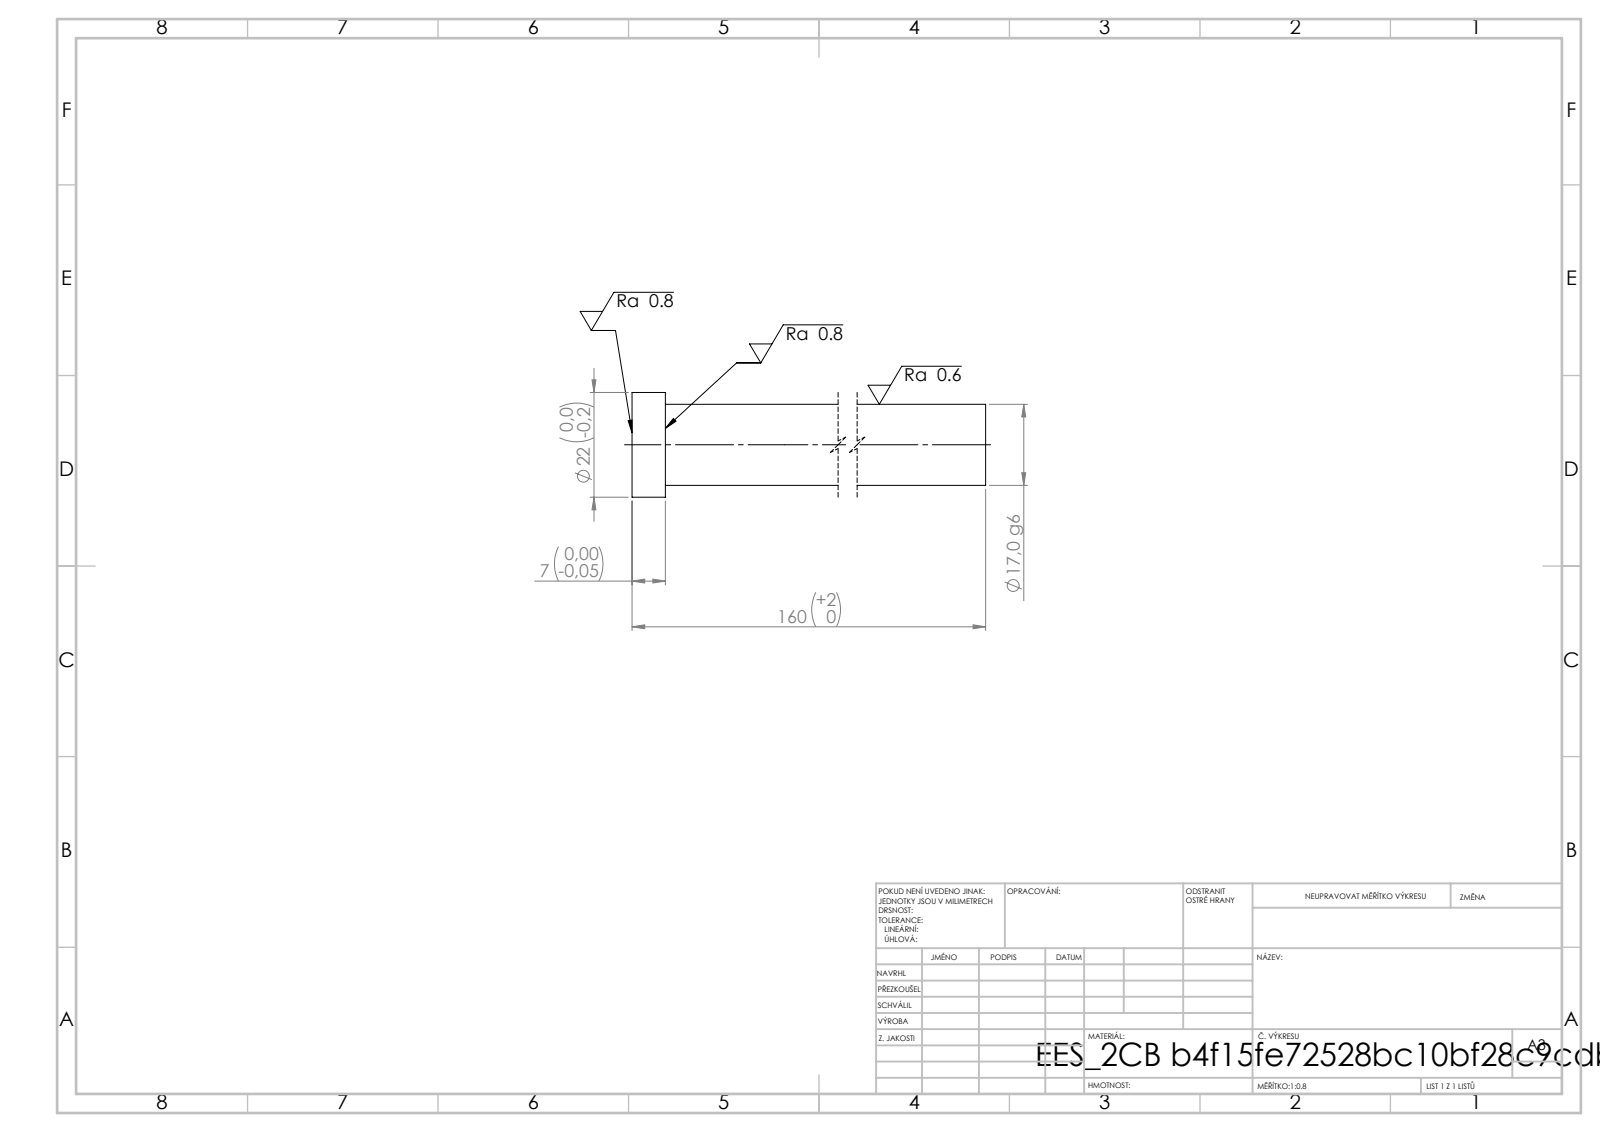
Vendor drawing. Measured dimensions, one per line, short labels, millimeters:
written by: SolidWorks 2019 (CONFIG_CONTROL_DESIGN)
unit: mm
bodies: 1 solid, 7 faces (3 planar, 4 cylindrical, 0 other)
size: 160 × 22 × 22
volume: 37 389 mm³; area: 9 415 mm²
bosses: 1× ⌀22, 1× ⌀17
face distances: 160, 7, 153
